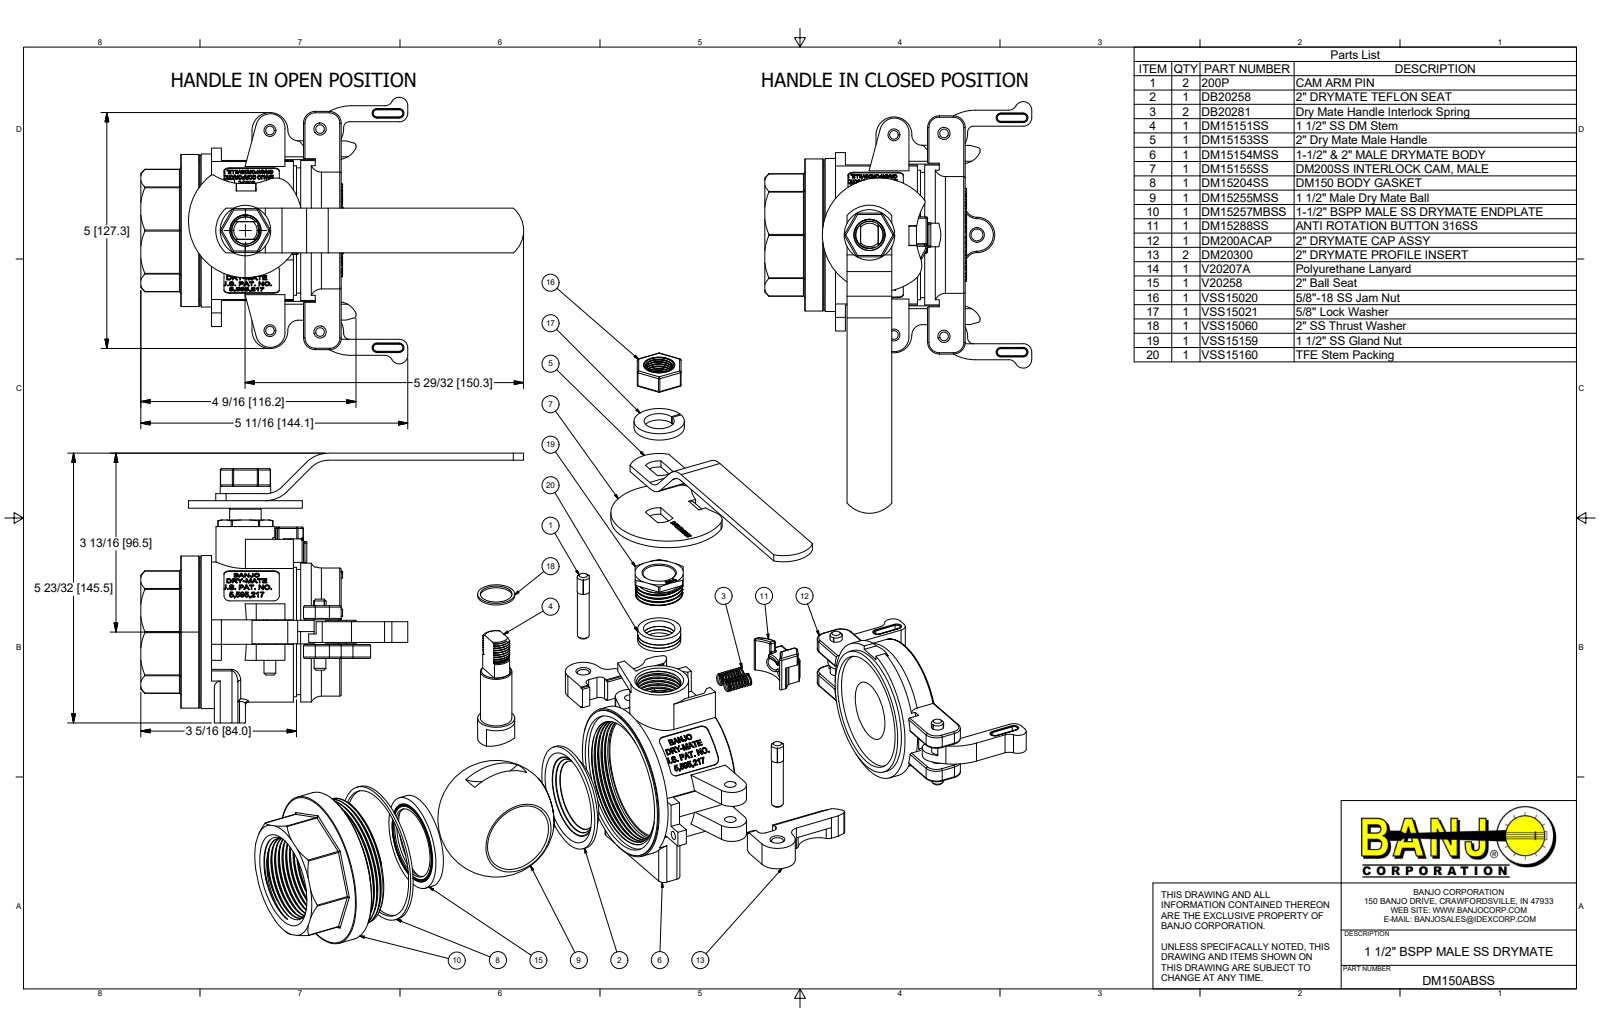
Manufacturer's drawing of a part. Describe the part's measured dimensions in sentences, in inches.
The part is named "DM150ABSS; DM15154MSS; DB20258; DB20281 (+8 more)". Its 3-D file was written by "Autodesk Inventor 2017 (AUTOMOTIVE_DESIGN)". It is 33 solids with 2559 faces: 1134 planar, 468 cylindrical and 957 other. Overall it measures 11.984 by 7.642 by 5.73 inches. Its volume is 26.05 cubic inches and its surface area 293.7 square inches. Round holes: 5 of diameter 0.25, 4 of diameter 0.256, 3 of diameter 0.125, 2 of diameter 1.5, 1 of diameter 0.18, 1 of diameter 0.58, 1 of diameter 0.64, 1 of diameter 0.662, 1 of diameter 0.67, 1 of diameter 0.676, 1 of diameter 0.69, 1 of diameter 0.84. Round bosses or shafts: 4 of diameter 0.26, 4 of diameter 0.249, 3 of diameter 0.28, 1 of diameter 3.23, 1 of diameter 3.19, 1 of diameter 2.975, 1 of diameter 2.97, 1 of diameter 2.945. Partial cylindrical surfaces (rounded edges, fillets, slot ends): 96 of radius 0.03, 8 of radius 0.06, 8 of radius 0.125, 6 of radius 0.18, 6 of radius 0.25, 4 of radius 0.025, 4 of radius 0.075, 4 of radius 0.12. The main face-to-face distances are 0.298, 0.86, 0.31, 0.15, 0.85, 1.17, 0.09, 0.822, 0.16, 1.02. The hole center spacings are 0.95, 1.646, 0.048, 1.065, 1.113, 2.187, 2.252, 2.266.
